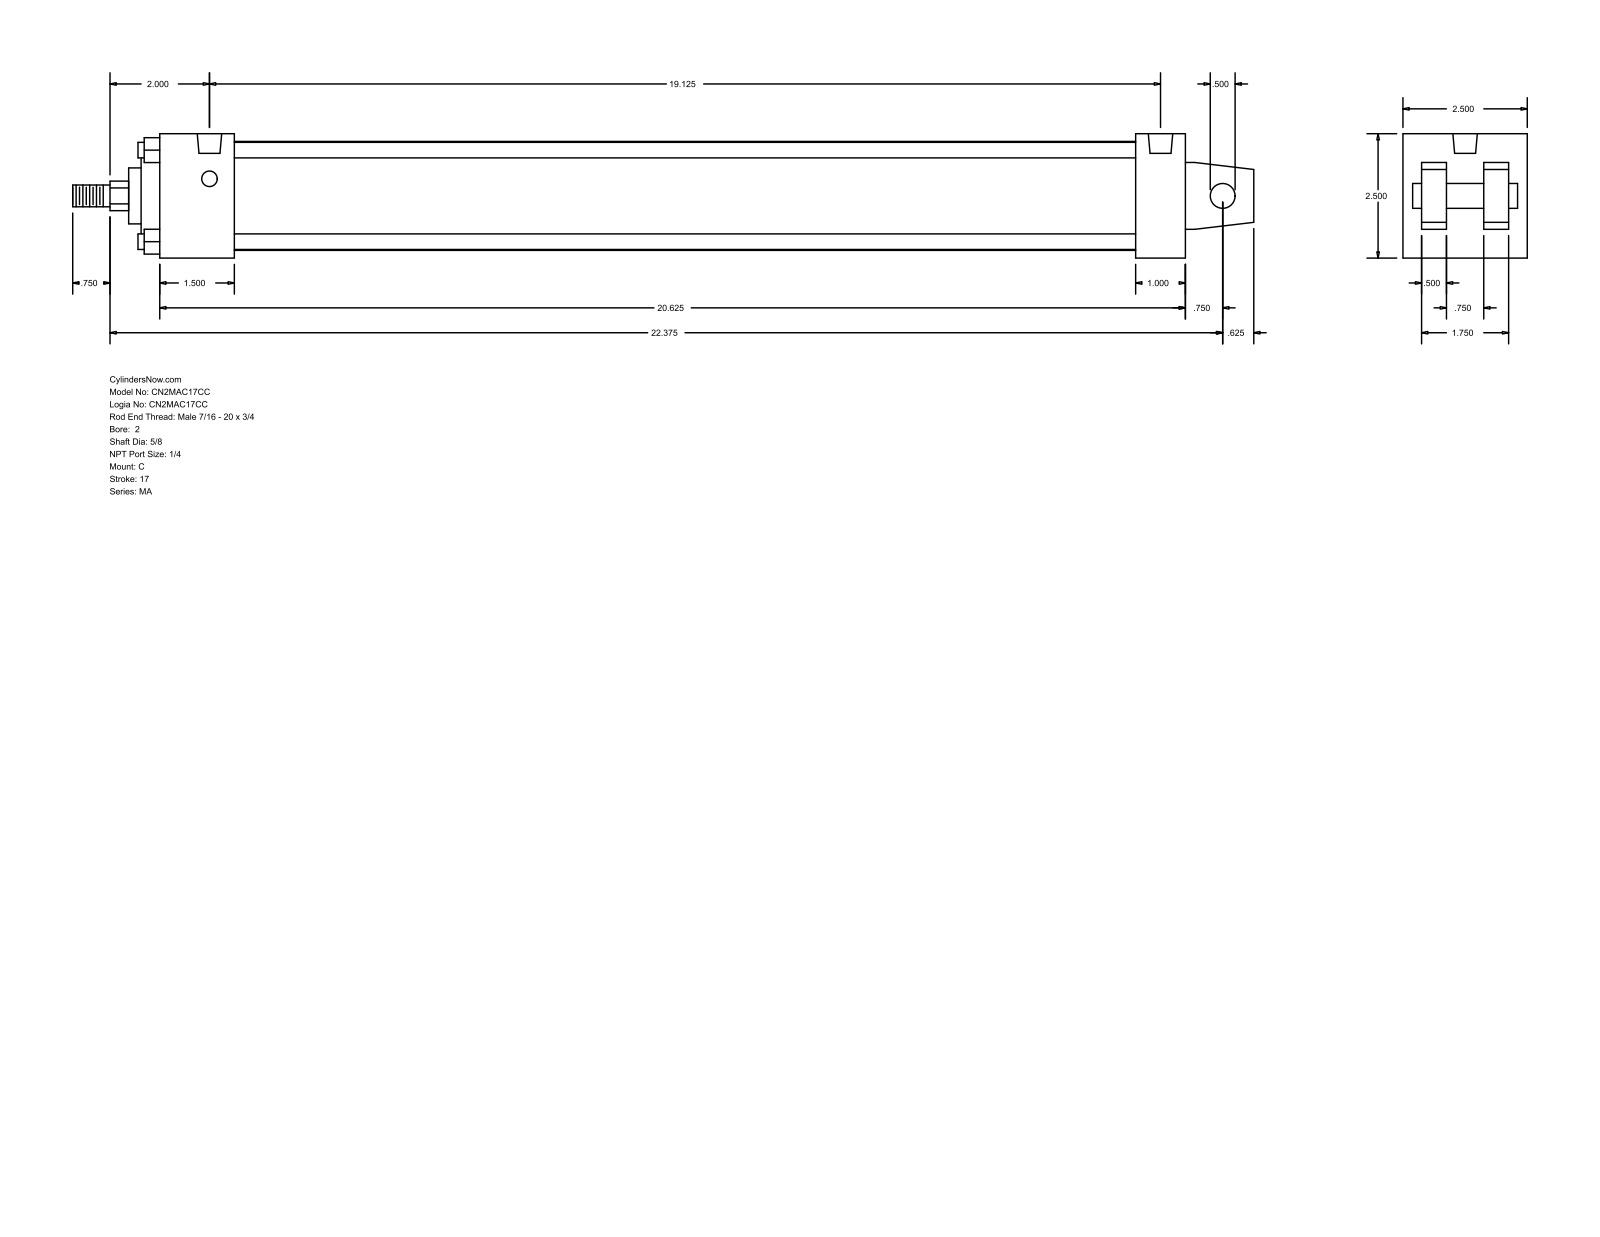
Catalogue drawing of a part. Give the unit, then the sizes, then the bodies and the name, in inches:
Units: inches
Overall size (bounding box): 23.75 × 2.5 × 2.5
Round holes (diameter × count): ⌀0.313 ×4, ⌀0.492 ×2
Round bosses / shafts (diameter × count): ⌀0.313 ×4, ⌀2.19 ×1, ⌀2 ×1, ⌀1.125 ×1, ⌀0.625 ×1, ⌀0.5 ×1, ⌀0.437 ×1
Partial cylindrical surfaces — rounded edges, fillets, slot ends (radius × count): R0.297 ×1
Main face-to-face distances: 2.5, 0.375, 0.5, 0.875, 1.625, 2.125, 1.25, 1.5, 20.625, 19.125
Hole centre spacings: 19.125
Bodies: 0 solids, 105 faces (77 planar, 28 cylindrical, 0 other)
Part name (STEP PRODUCT): MA_C__0200_0.625
STEP written by: GSSL Pune (CONFIG_CONTROL_DESIGN)
